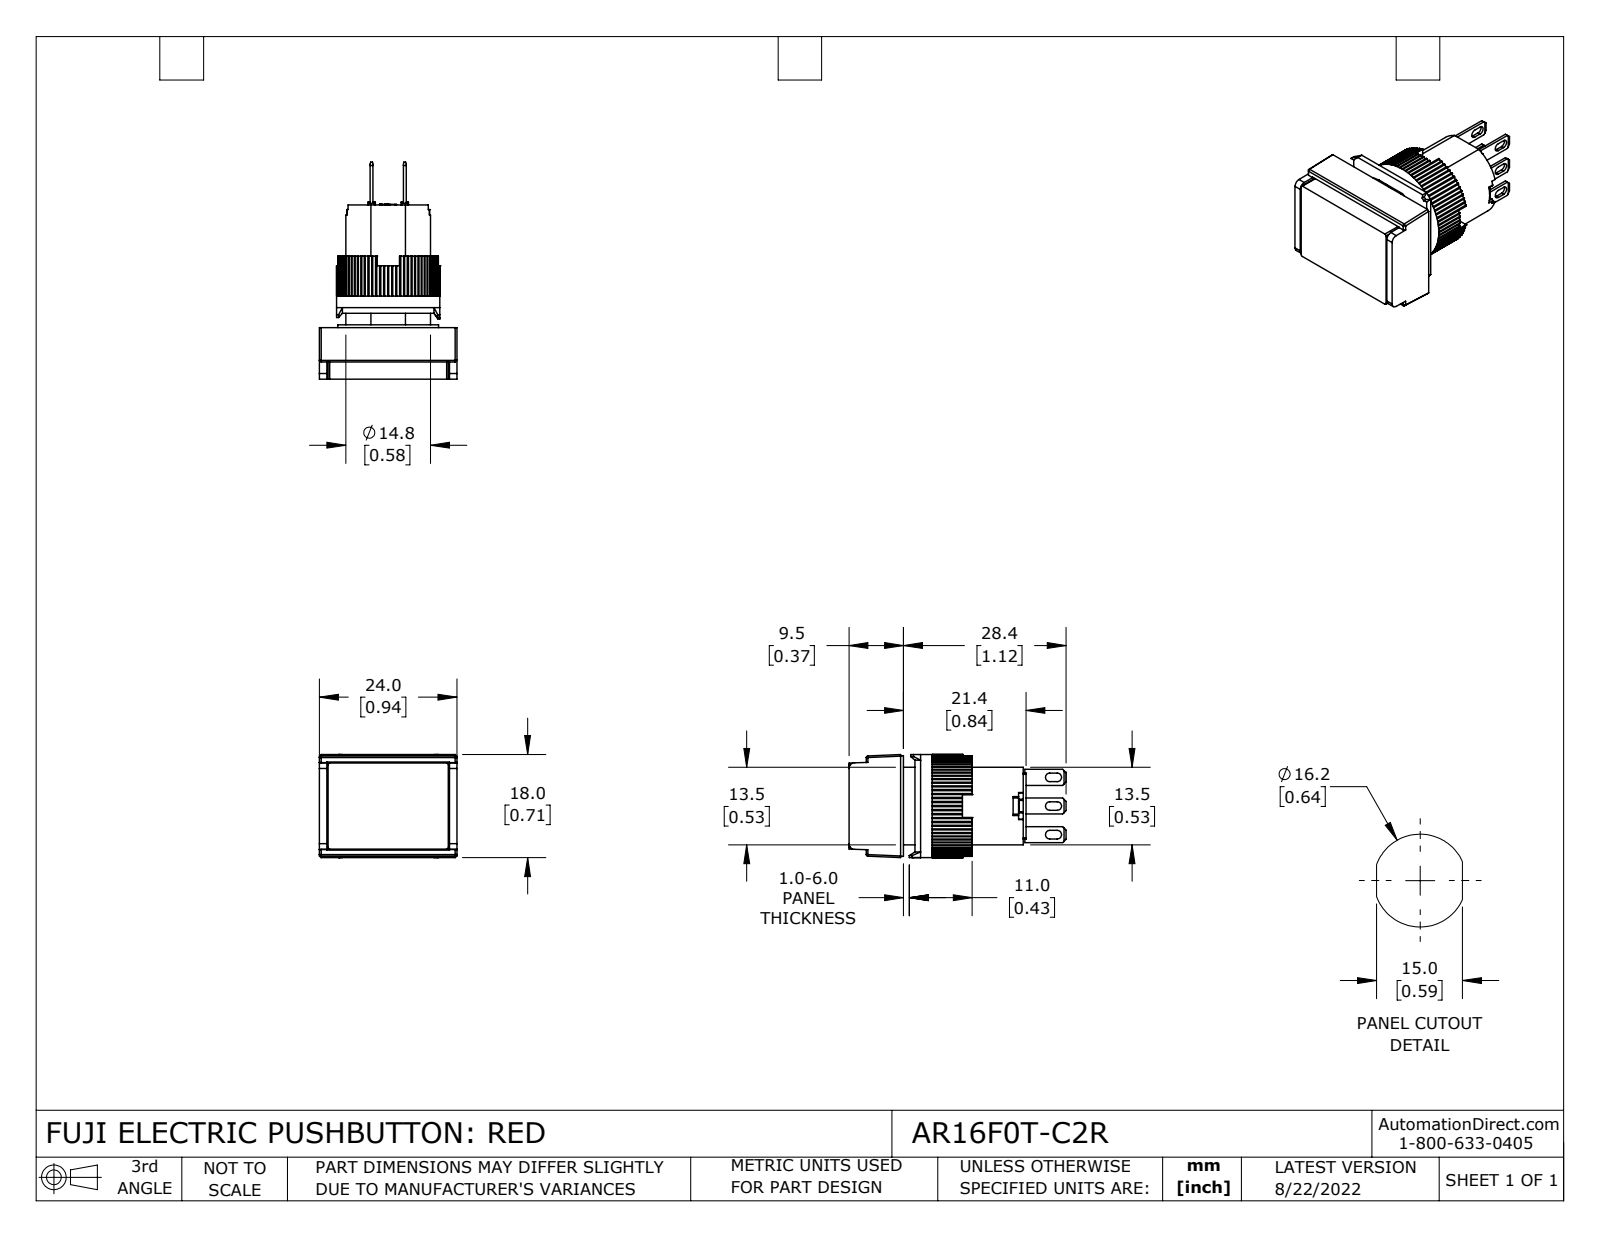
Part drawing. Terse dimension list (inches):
name: AR16F0T-C2R
written by: SolidWorks 2021 (CONFIG_CONTROL_DESIGN)
unit: in
bodies: 12 solids, 813 faces (632 planar, 177 cylindrical, 4 other)
size: 1.492 × 0.945 × 0.709
volume: 0.443 in³; area: 9.124 in²
holes: 1× ⌀0.543, 1× ⌀0.583
bosses: 1× ⌀0.709, 1× ⌀0.693
rounds: 80× R0.01, 12× R0.008, 6× R0.012, 6× R0.03, 2× R0.039
face distances: 0.213, 0.354, 0.142, 0.492, 0.35, 0.138, 0.02, 0.843, 0.059, 0.453
